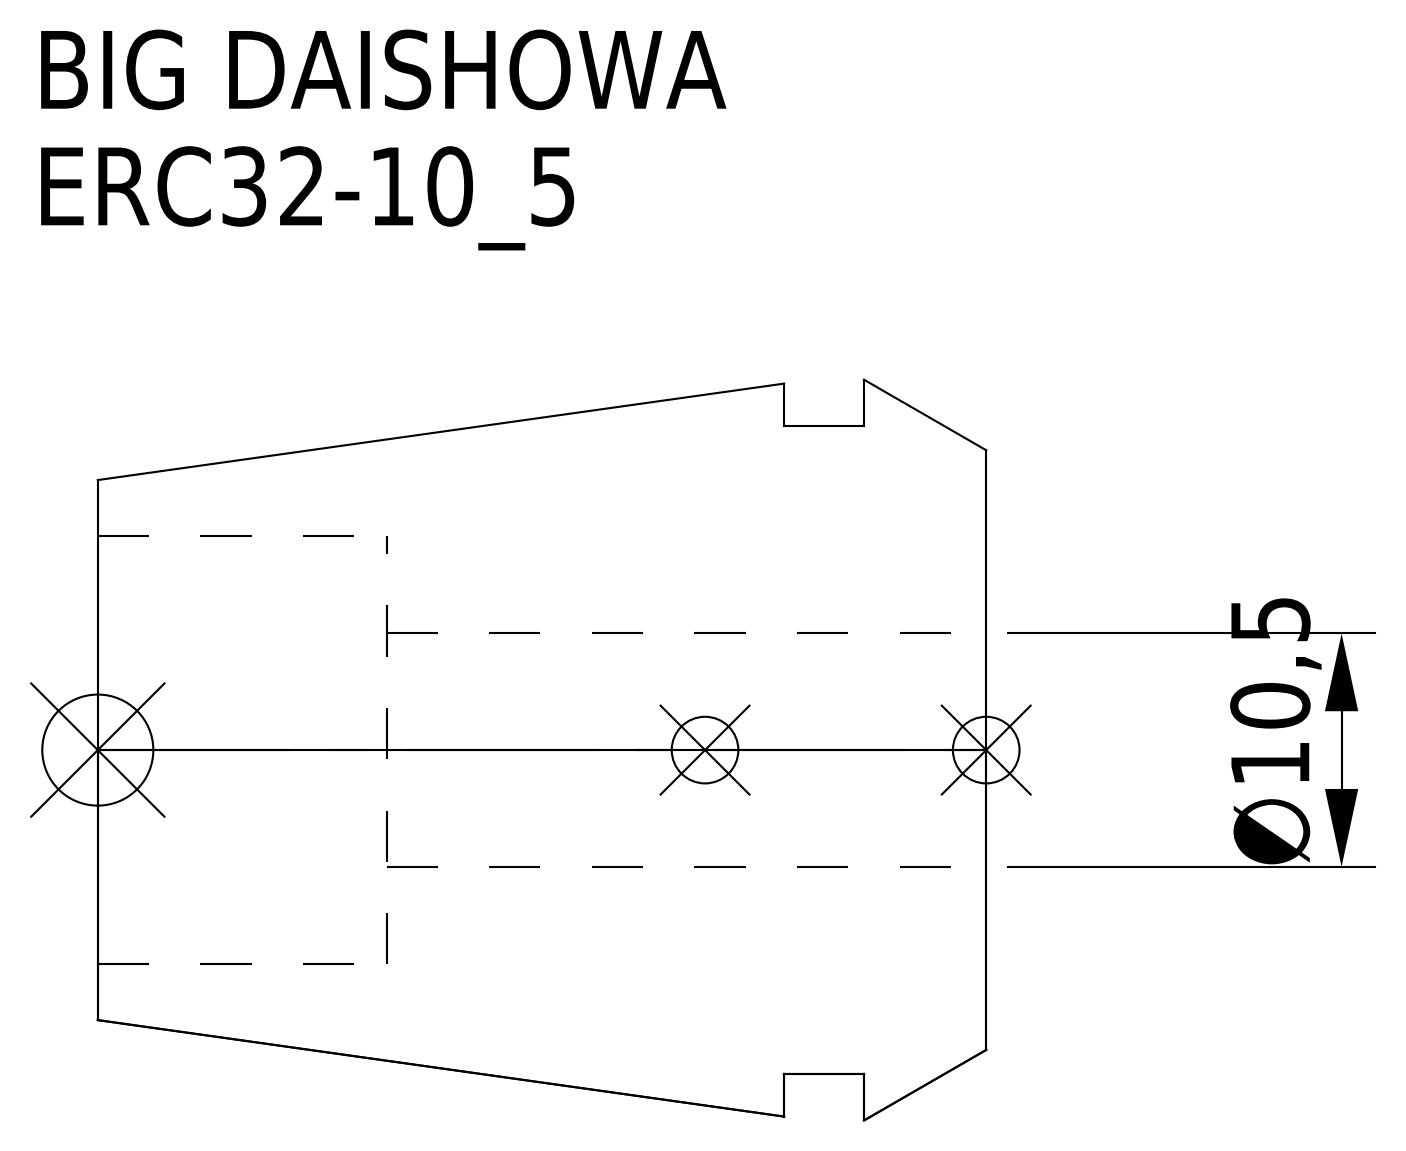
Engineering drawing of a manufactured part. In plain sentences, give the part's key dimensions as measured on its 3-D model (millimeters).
The part is named "ERC32-10_5". Its 3-D file was written by "CREO PARAMETRIC BY PTC INC, 2016380 (AUTOMOTIVE_DESIGN)". It is 1 solid with 15 faces: 5 planar, 6 cylindrical and 4 other. Overall it measures 40 by 33.35 by 33.35 millimeters. Its volume is 20 301 cubic millimeters and its surface area 6 674 square millimeters. Round holes: 1 of diameter 10.5, 1 of diameter 19.3. Round bosses or shafts: 1 of diameter 29.2. The main face-to-face distances are 27, 5.5, 21.5, 9.1, 3.6, 17.9, 40, 34.5, 30.9, 13.
